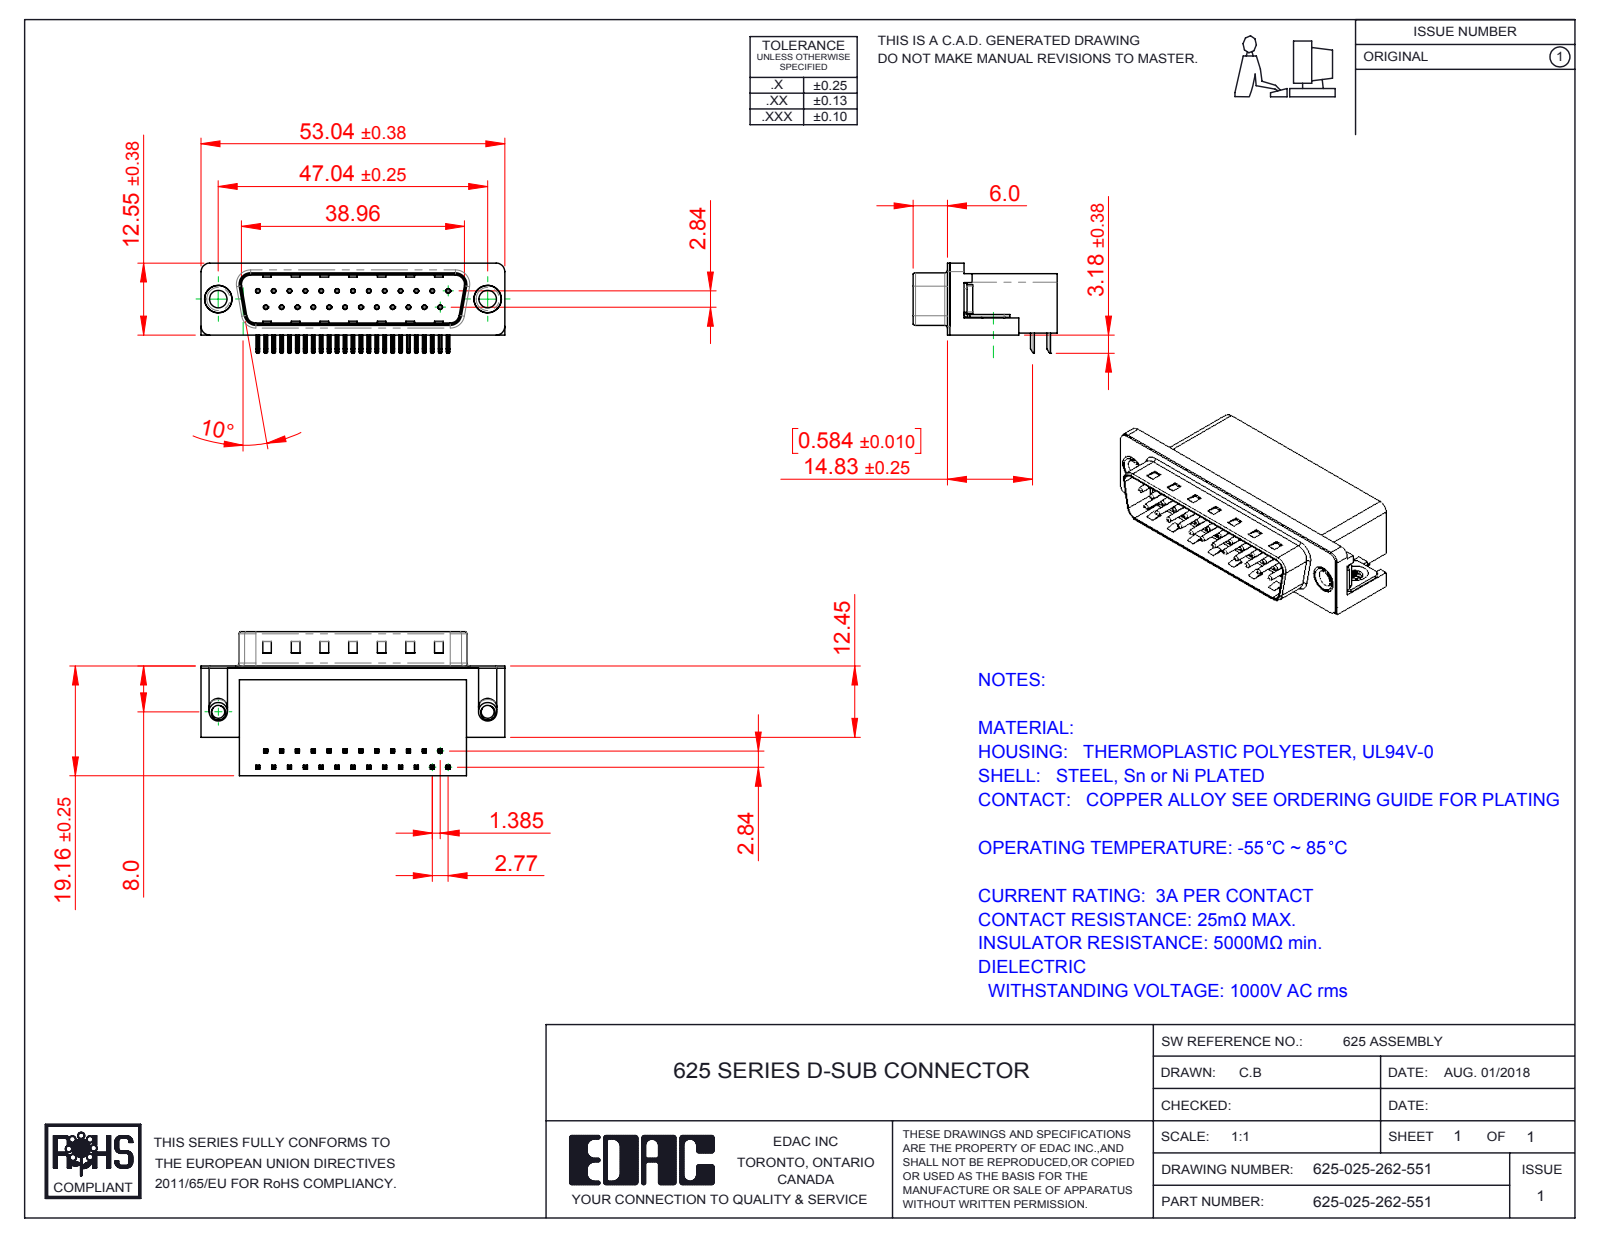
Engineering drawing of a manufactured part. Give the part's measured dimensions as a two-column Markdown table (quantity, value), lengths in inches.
| quantity | value |
| --- | --- |
| part name | 625 Housing_25 Socket; 625 Shell_25 Socket; 625 Contact Top; 625 4-40 Threaded Board Mount (+3 more) |
| STEP written by | SolidWorks 2016 (CONFIG_CONTROL_DESIGN) |
| units | inches |
| bodies | 31 solids, 2257 faces (1407 planar, 655 cylindrical, 195 other) |
| overall size | 2.088 × 0.991 × 0.619 |
| volume | 0.559 in³ |
| surface area | 13.82 in² |
| round holes (diameter × count) | 0.014 × 25, 0.031 × 25, 0.089 × 2, 0.12 × 2, 0.157 × 2, 0.189 × 2, 0.197 × 2 |
| round bosses / shafts (diameter × count) | 0.03 × 25, 0.193 × 2, 0.187 × 2, 0.152 × 2, 0.128 × 2 |
| partial cylindrical surfaces (radius × count) | 0.01 × 108, 0.005 × 50, 0.039 × 16, 0.02 × 9, 0.063 × 8, 0.059 × 7, 0.035 × 4, 0.079 × 4 |
| main face-to-face distances | 0.016, 0.407, 0.739, 0.083, 0.345, 0.412, 0.428, 0.067, 0.754, 0.398 |
| hole center spacings | 0.124, 0.109, 0.436, 0.218, 0.327, 0.198, 0.545, 0.294 |
